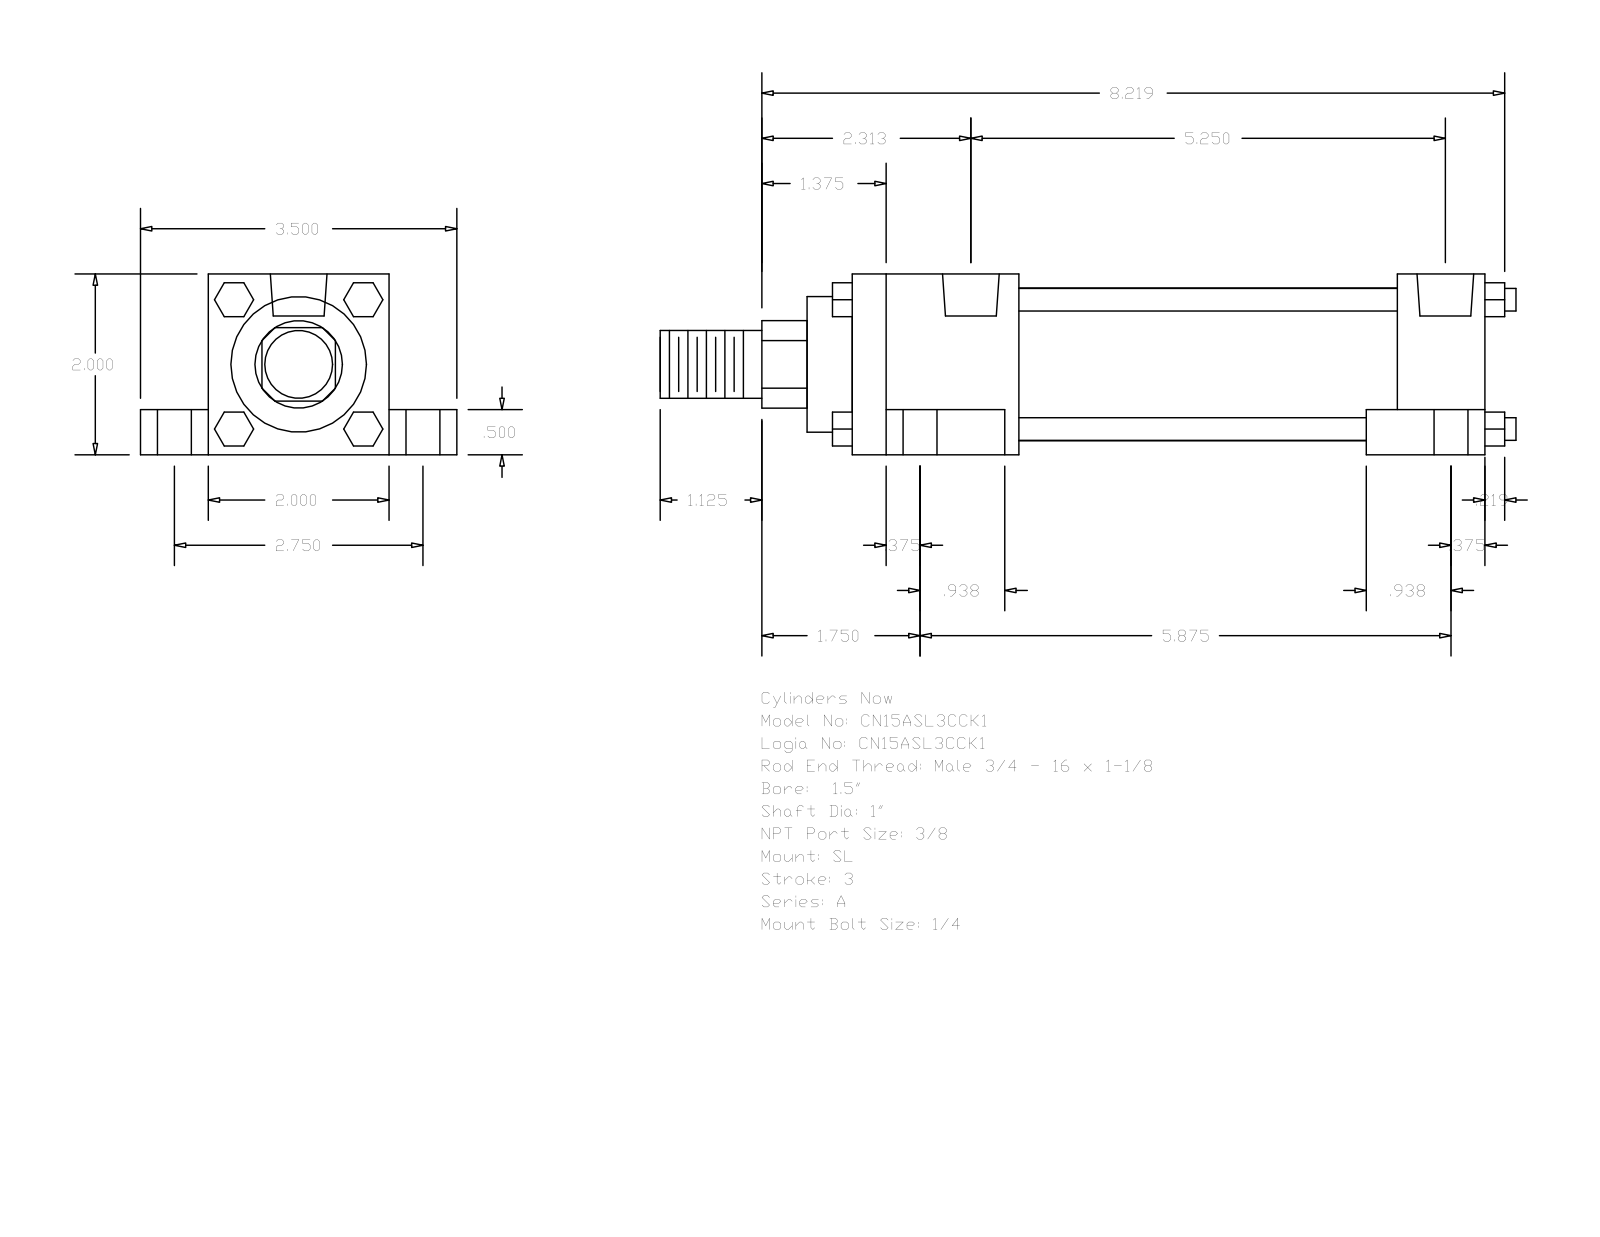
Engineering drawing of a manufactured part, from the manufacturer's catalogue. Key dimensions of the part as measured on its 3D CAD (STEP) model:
Part name (STEP PRODUCT): A_SL__0150_1
STEP written by: GSSL Pune (CONFIG_CONTROL_DESIGN)
Units: millimetres
Bodies: 0 solids, 148 faces (112 planar, 36 cylindrical, 0 other)
Overall size (bounding box): 240.51 × 88.9 × 50.8
Round holes (diameter × count): ⌀5.56 ×4, ⌀9.53 ×4, ⌀15.88 ×4, ⌀15.93 ×2
Round bosses / shafts (diameter × count): ⌀6.35 ×4, ⌀42.93 ×1, ⌀38.1 ×1, ⌀25.4 ×1, ⌀19.05 ×1
Partial cylindrical surfaces — rounded edges, fillets, slot ends (radius × count): R12.29 ×1
Main face-to-face distances: 50.8, 12.7, 38.1, 19.05, 69.85, 9.52, 177.8, 33.34, 153.19, 24.61
Hole centre spacings: 3.97, 34.96, 35.36, 37.73, 39.41, 69.84, 125.41, 129.38
